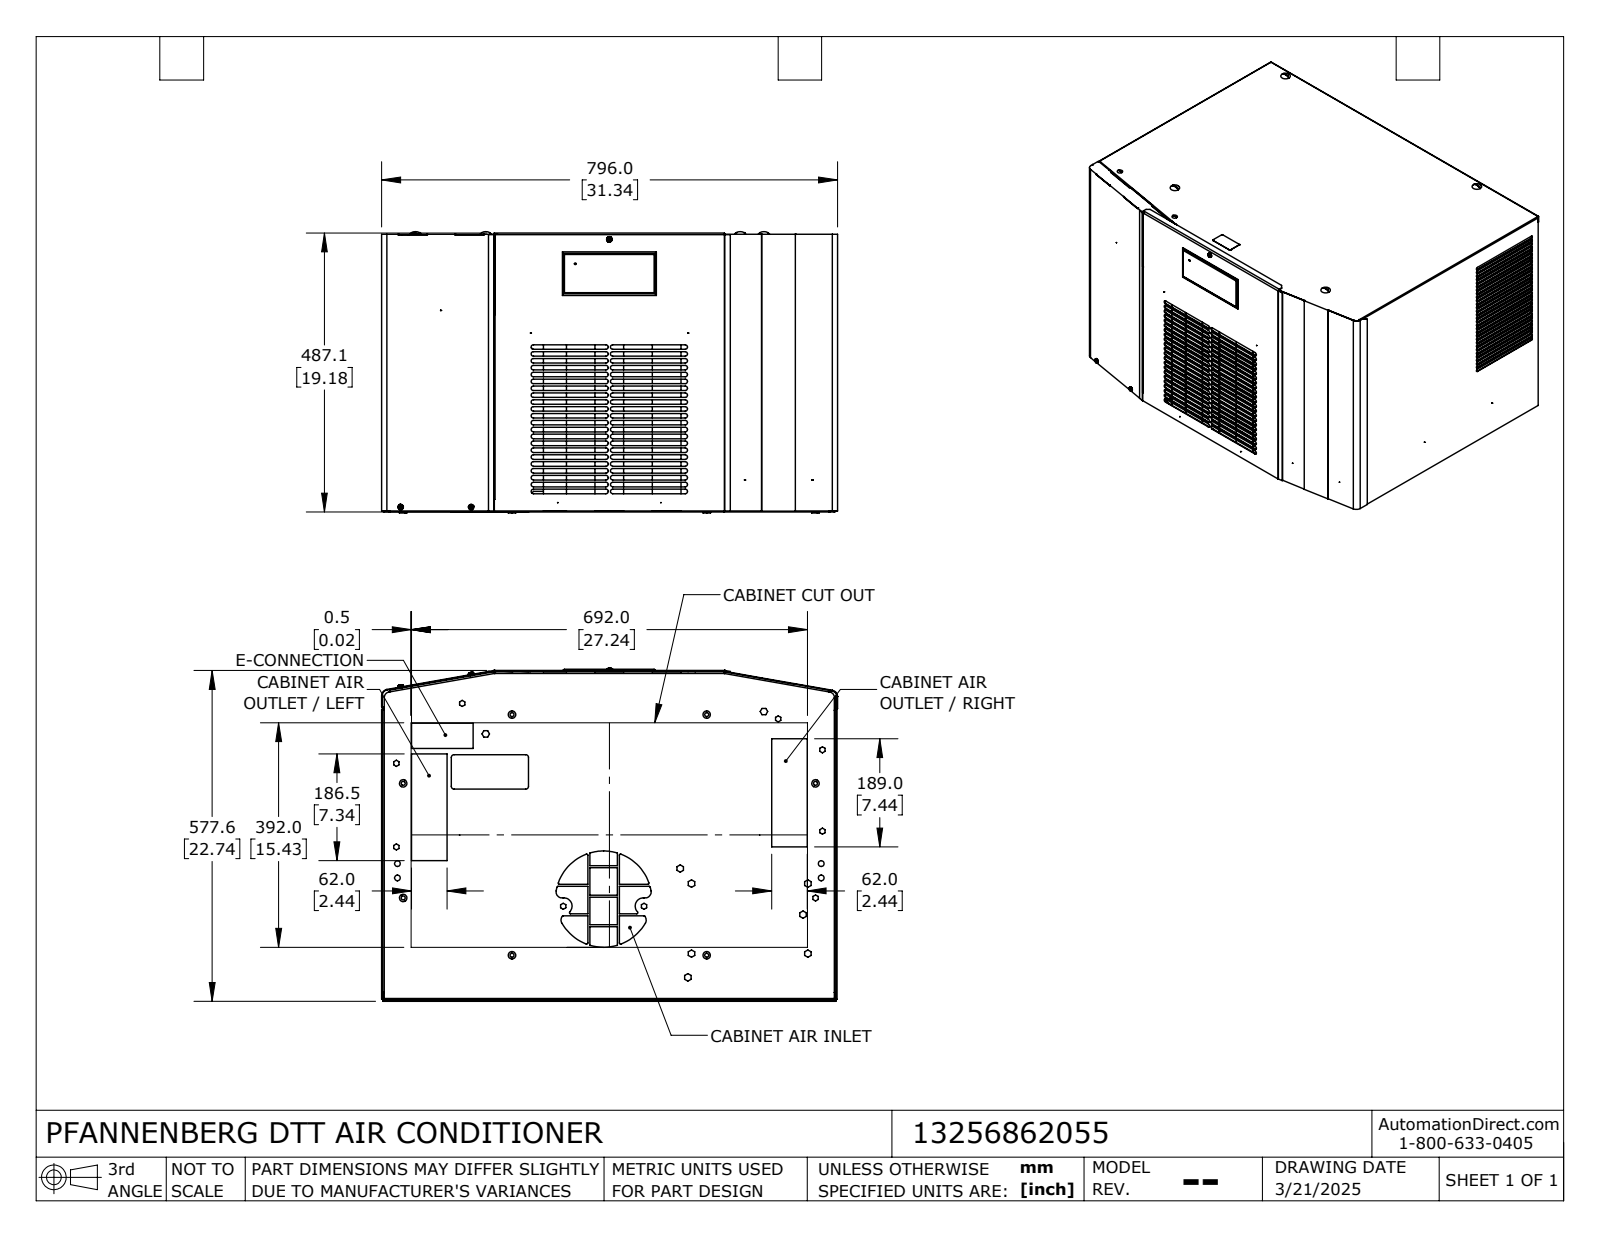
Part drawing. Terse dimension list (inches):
name: 13256862055_Default
written by: SolidWorks 2024 (CONFIG_CONTROL_DESIGN)
unit: in
bodies: 1 solid, 2034 faces (1347 planar, 571 cylindrical, 116 other)
size: 31.339 × 22.884 × 19.33
volume: 13 045 in³; area: 5 862 in²
holes: 14× ⌀0.02, 10× ⌀0.394, 7× ⌀0.272, 5× ⌀0.138, 3× ⌀0.079, 3× ⌀0.094, 3× ⌀0.177, 3× ⌀0.213, 2× ⌀0.075, 2× ⌀0.172, 2× ⌀0.276, 2× ⌀0.48
bosses: 7× ⌀0.512, 6× ⌀0.197, 5× ⌀0.136, 4× ⌀0.315, 3× ⌀0.302, 2× ⌀0.19, 2× ⌀0.157, 1× ⌀0.118
rounds: 88× R0.157, 68× R0.118, 21× R0.079, 9× R0.043, 9× R0.122, 8× R0.035, 8× R0.063, 7× R0.102
face distances: 0.039, 31.22, 0.079, 31.181, 31.26, 19.094, 31.299, 31.142, 0.059, 22.661
hole spacings: 3.504, 7.008, 7.874, 4.921, 10.512, 0.551, 0.602, 0.984
